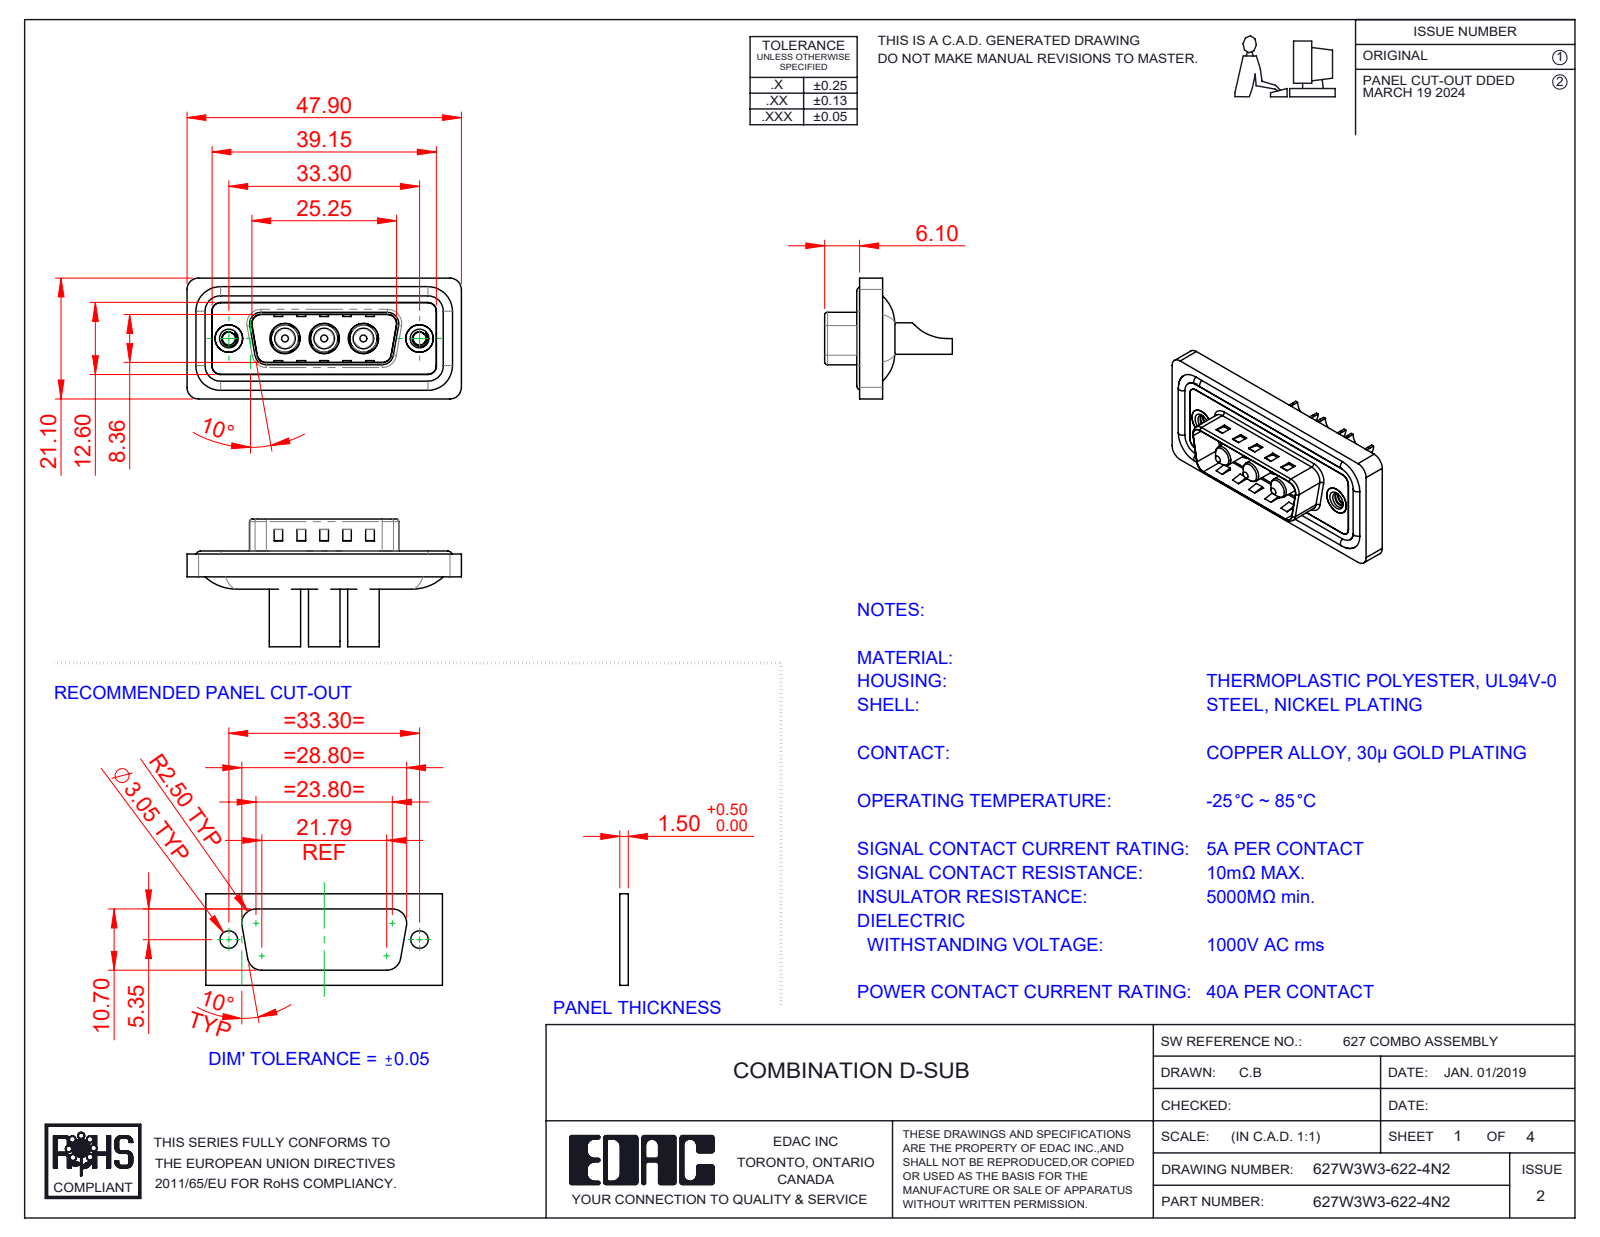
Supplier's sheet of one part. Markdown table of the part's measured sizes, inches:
| quantity | value |
| --- | --- |
| part name | 627Combo Housing_3W3; 627Combo Threaded Rivet_2; 627Combo Shell Front_15 Contacts; Power Pin_40A SC (+3 more) |
| STEP written by | SolidWorks 2023 (CONFIG_CONTROL_DESIGN) |
| units | inches |
| bodies | 13 solids, 576 faces (213 planar, 244 cylindrical, 119 other) |
| overall size | 1.886 × 0.878 × 0.831 |
| volume | 0.348 in³ |
| surface area | 14.22 in² |
| round holes (diameter × count) | 0.181 × 3, 0.191 × 3, 0.209 × 3, 0.089 × 2, 0.157 × 2, 0.189 × 2, 0.197 × 2 |
| round bosses / shafts (diameter × count) | 0.063 × 4, 0.217 × 3, 0.205 × 3, 0.187 × 3, 0.148 × 3, 0.142 × 3, 0.193 × 2 |
| partial cylindrical surfaces (radius × count) | 0.059 × 26, 0.079 × 20, 0.02 × 8, 0.063 × 8, 0.01 × 4, 0.024 × 4, 0.026 × 4, 0.035 × 4 |
| main face-to-face distances | 0.016, 0.043, 0.02, 0.063, 0.122, 0.114, 0.059, 0.032, 0.377, 0.098 |
| hole center spacings | 0.27, 0.386, 0.656, 0.925, 0.539, 1.311 |
